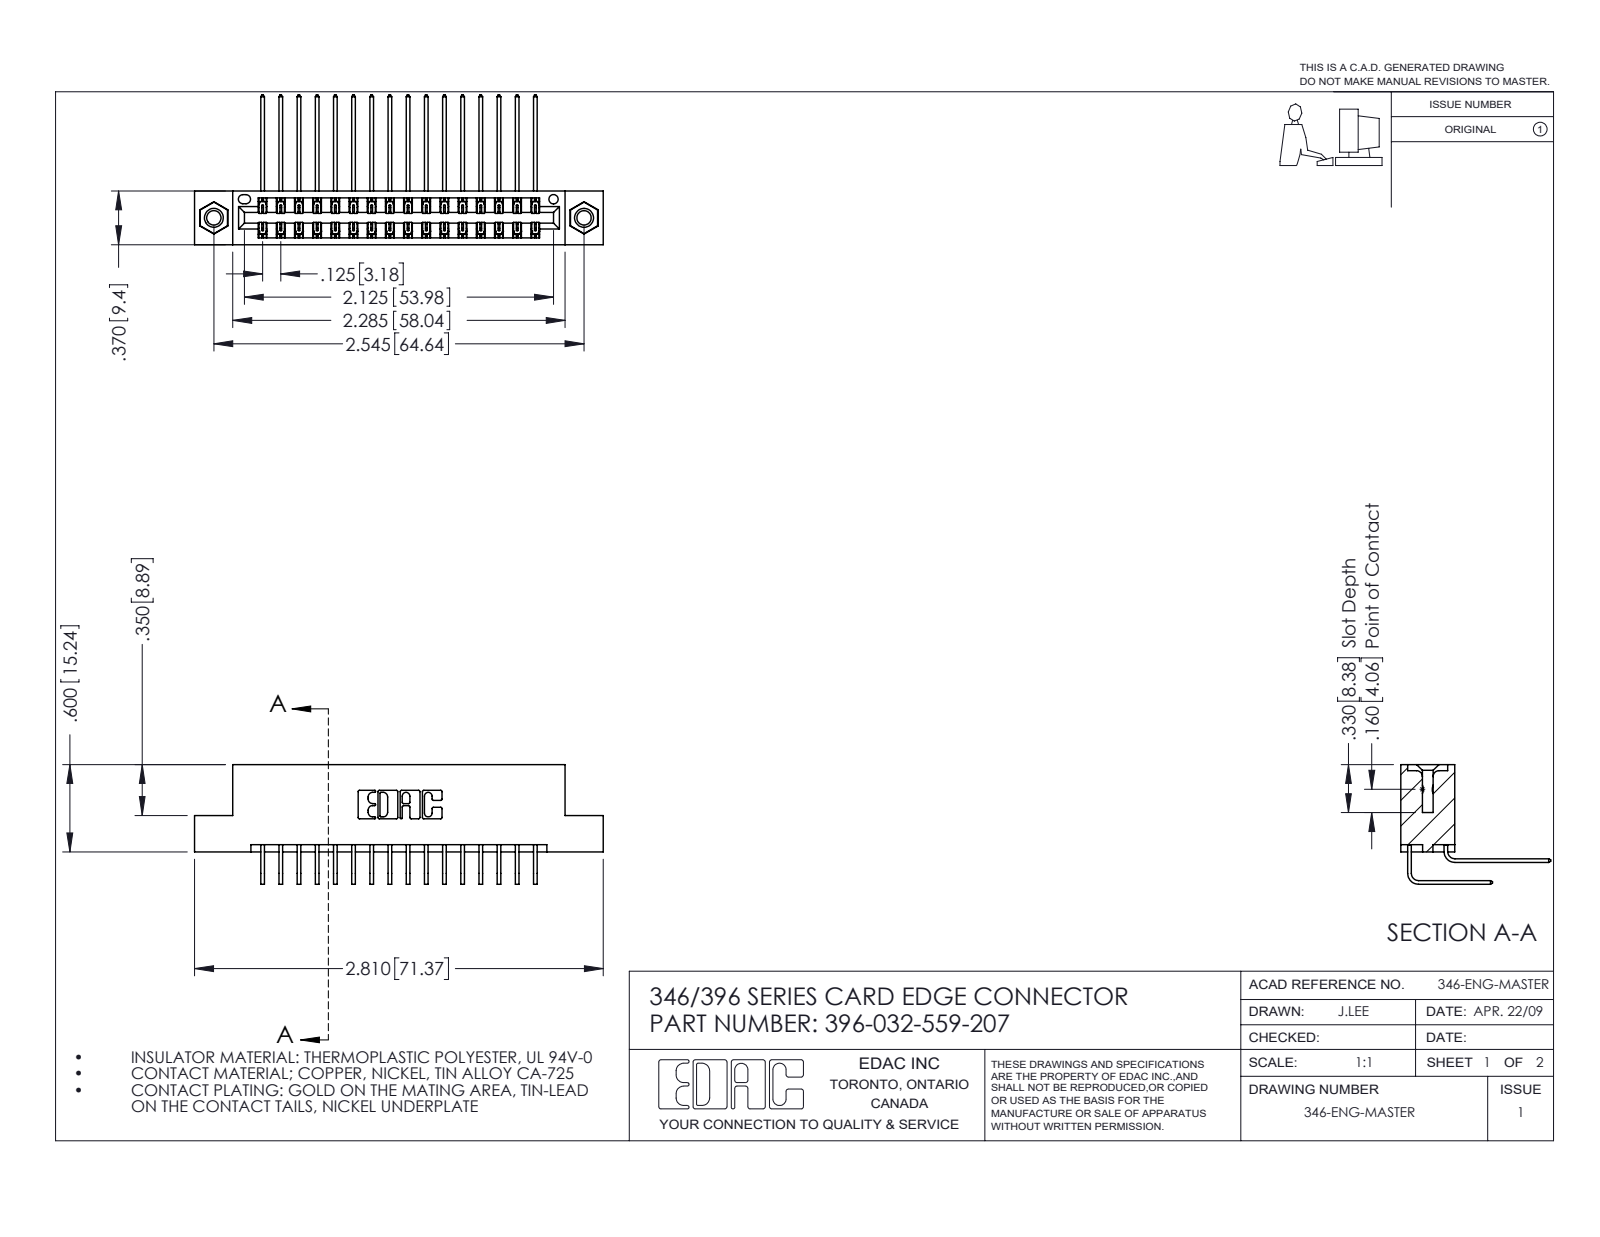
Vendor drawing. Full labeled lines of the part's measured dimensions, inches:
Part name (STEP PRODUCT): 346 Part_Flush Mounting Lugs - 0.156 Dia-TI; 345-292-001_558 559 Tail - 1; 345-292-001_559 Tail - 2; 396-032-559-207 (+1 more)
STEP written by: SolidWorks 2016 (CONFIG_CONTROL_DESIGN)
Units: inches
Bodies: 35 solids, 1910 faces (1292 planar, 602 cylindrical, 16 other)
Overall size (bounding box): 2.81 × 1.03 × 0.823
Volume: 0.423 in³ · Surface area: 15.55 in²
Round holes (diameter × count): ⌀0.098 ×2, ⌀0.125 ×2, ⌀0.156 ×2, ⌀0.064 ×1
Round bosses / shafts (diameter × count): ⌀0.155 ×2
Partial cylindrical surfaces — rounded edges, fillets, slot ends (radius × count): R0.006 ×48, R0.01 ×22, R0.007 ×6, R0.031 ×6, R0.026 ×3, R0.014 ×2, R0.022 ×2, R0.024 ×2
Main face-to-face distances: 0.048, 0.322, 0.25, 0.025, 0.37, 0.072, 0.298, 0.275, 0.148, 0.222
Hole centre spacings: 0.246, 2.338, 2.545
